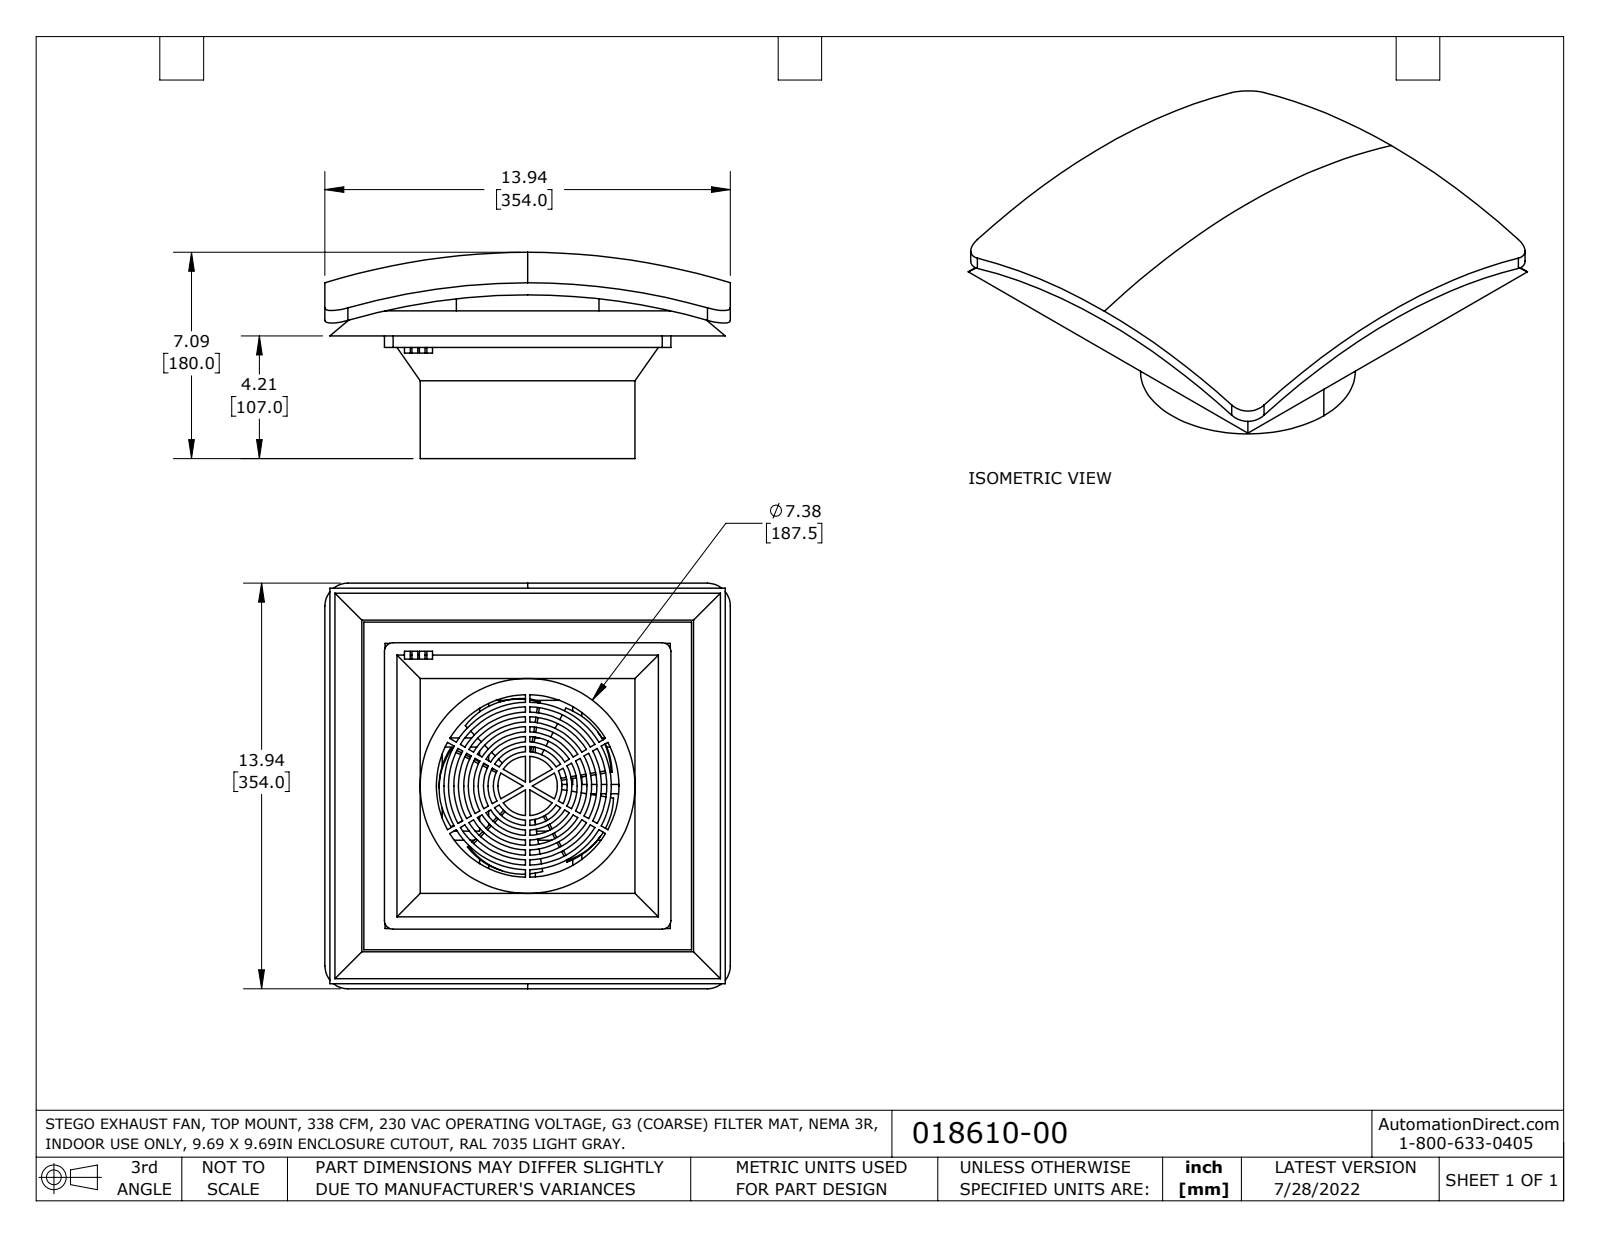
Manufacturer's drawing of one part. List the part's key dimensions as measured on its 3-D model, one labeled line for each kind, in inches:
Part name (STEP PRODUCT): 018610-00_Default
STEP written by: SolidWorks 2021 (CONFIG_CONTROL_DESIGN)
Units: inches
Bodies: 1 solid, 480 faces (361 planar, 115 cylindrical, 4 other)
Overall size (bounding box): 13.937 × 13.937 × 7.087
Volume: 286.6 in³ · Surface area: 1 389 in²
Round holes (diameter × count): ⌀2.039 ×1, ⌀2.718 ×1, ⌀3.398 ×1, ⌀4.078 ×1, ⌀4.758 ×1, ⌀5.437 ×1, ⌀6.275 ×1
Round bosses / shafts (diameter × count): ⌀7.382 ×1, ⌀5.752 ×1, ⌀5.073 ×1, ⌀4.393 ×1, ⌀3.713 ×1, ⌀3.033 ×1, ⌀2.354 ×1, ⌀2.196 ×1
Partial cylindrical surfaces — rounded edges, fillets, slot ends (radius × count): R3.043 ×5, R0.295 ×4, R0.787 ×4
Main face-to-face distances: 0.431, 0.862, 0.109, 0.157, 0.172, 0.259, 0.69, 0.728, 10.531, 1.601
